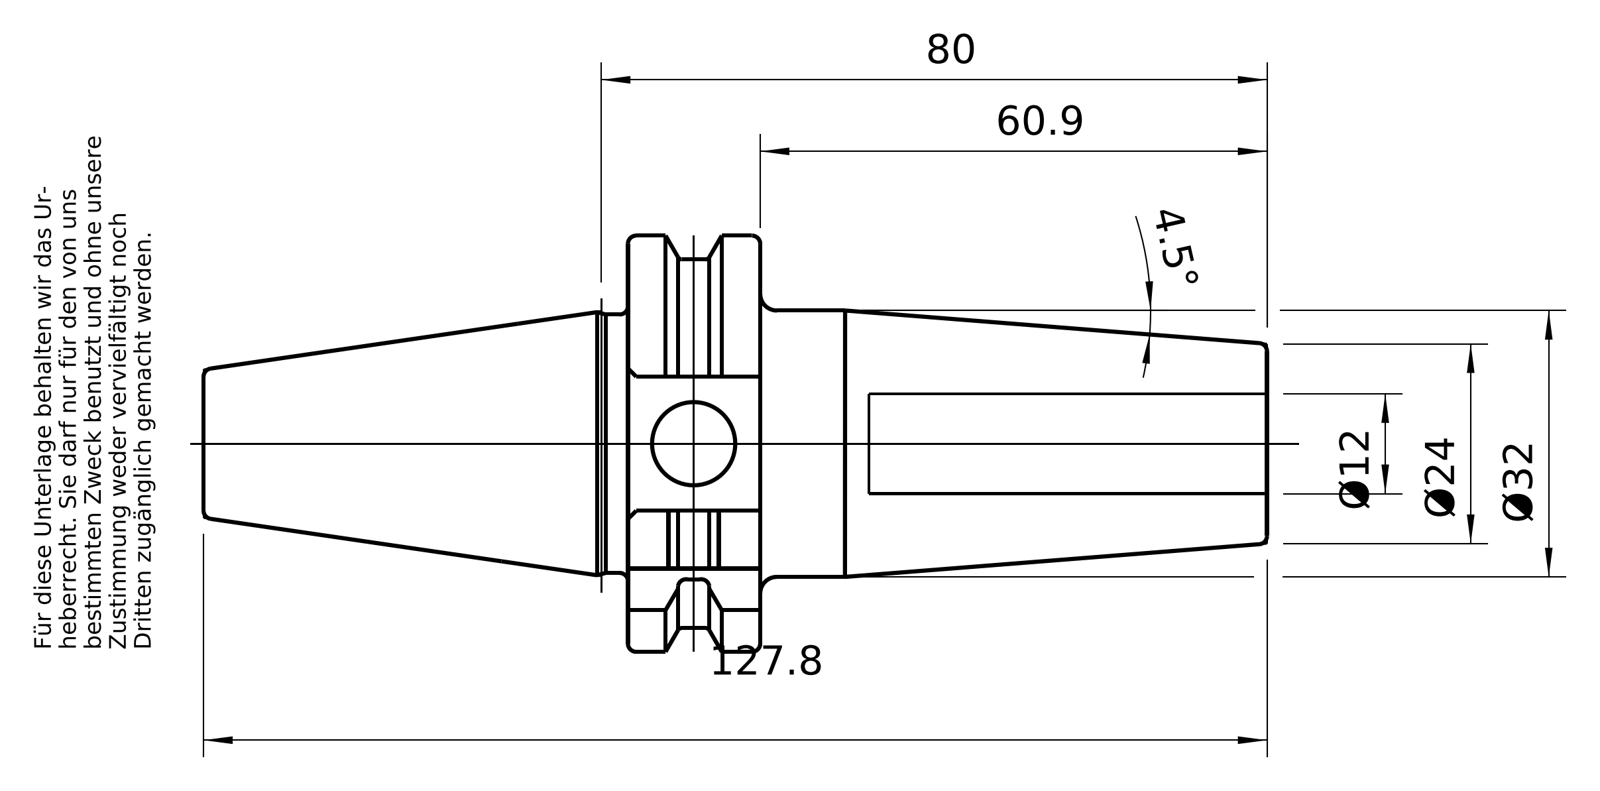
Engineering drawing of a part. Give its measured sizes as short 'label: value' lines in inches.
name: 30-440-12
written by: PRO/ENGINEER BY PARAMETRIC TECHNOLOGY CORPORATION, 2010430 (CONFIG_CONTROL_DESIGN)
unit: in
bodies: 1 solid, 92 faces (21 planar, 23 cylindrical, 48 other)
size: 5.026 × 1.968 × 1.863
volume: 5.054 in³; area: 28.99 in²
holes: 1× ⌀0.398, 1× ⌀0.472, 1× ⌀0.512, 1× ⌀0.531
bosses: 1× ⌀1.26, 1× ⌀1.222, 1× ⌀0.473
rounds: 1× R0.867, 1× R0.984
face distances: 0.624, 2.4, 3.024, 1.382, 0.634, 1.173, 0.549, 1.85, 0.274, 0.907
